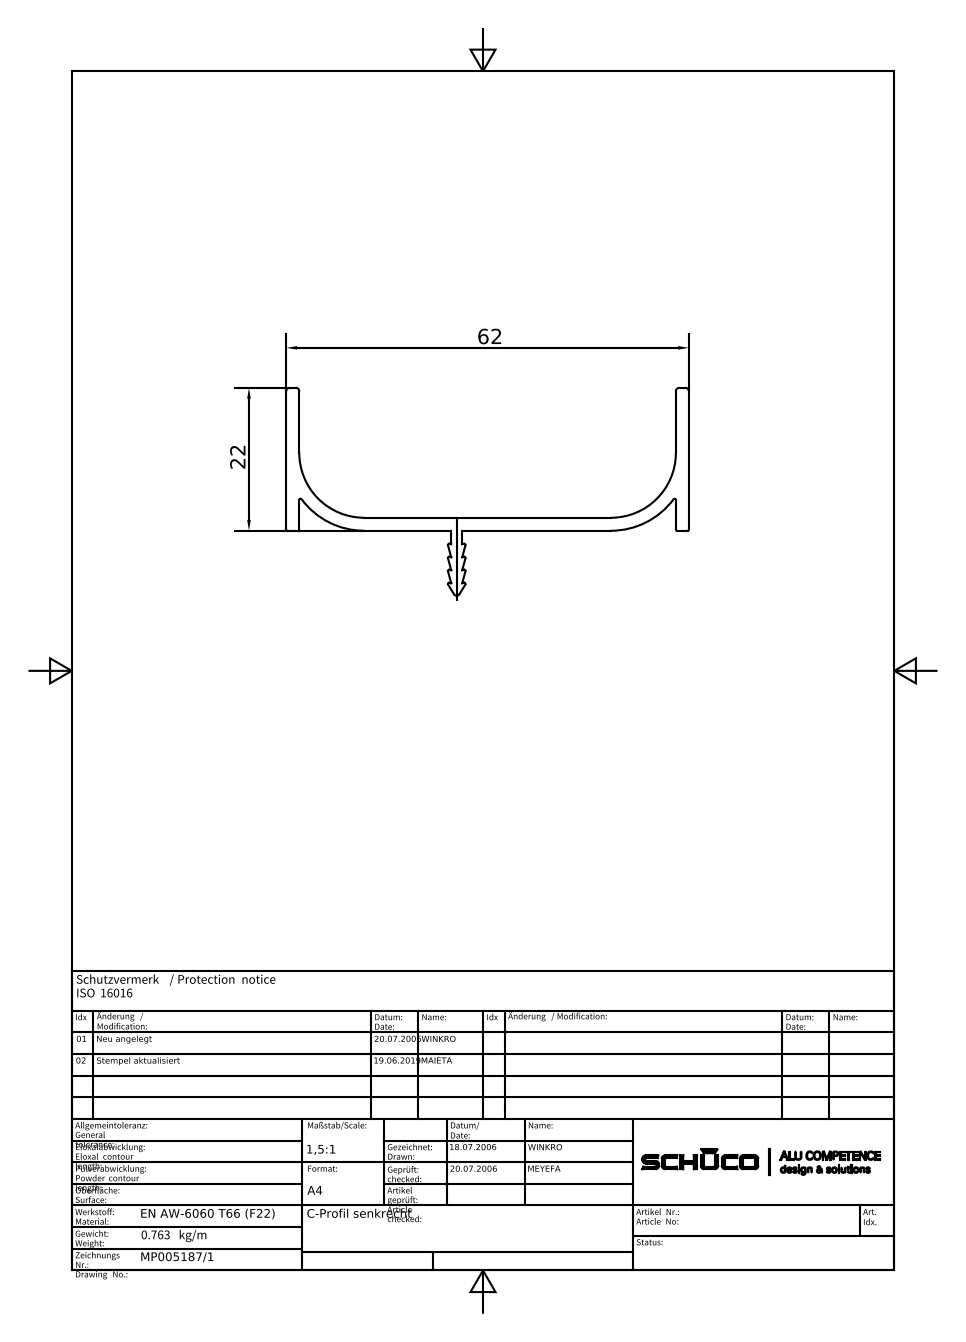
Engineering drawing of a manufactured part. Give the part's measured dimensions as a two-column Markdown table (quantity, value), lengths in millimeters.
| quantity | value |
| --- | --- |
| part name | MP00518701 |
| STEP written by | Autodesk Inventor 2015 (AUTOMOTIVE_DESIGN) |
| units | millimeters |
| bodies | 1 solid, 56 faces (33 planar, 23 cylindrical, 0 other) |
| overall size | 62 × 32 × 10 |
| volume | 2 354 mm³ |
| surface area | 2 819 mm² |
| partial cylindrical surfaces (radius × count) | 0.2 × 14, 0.5 × 5, 10 × 2, 12 × 2 |
| main face-to-face distances | 2, 60, 10, 62, 58, 0.52, 36.6, 34.6, 23.4, 25.4 |
